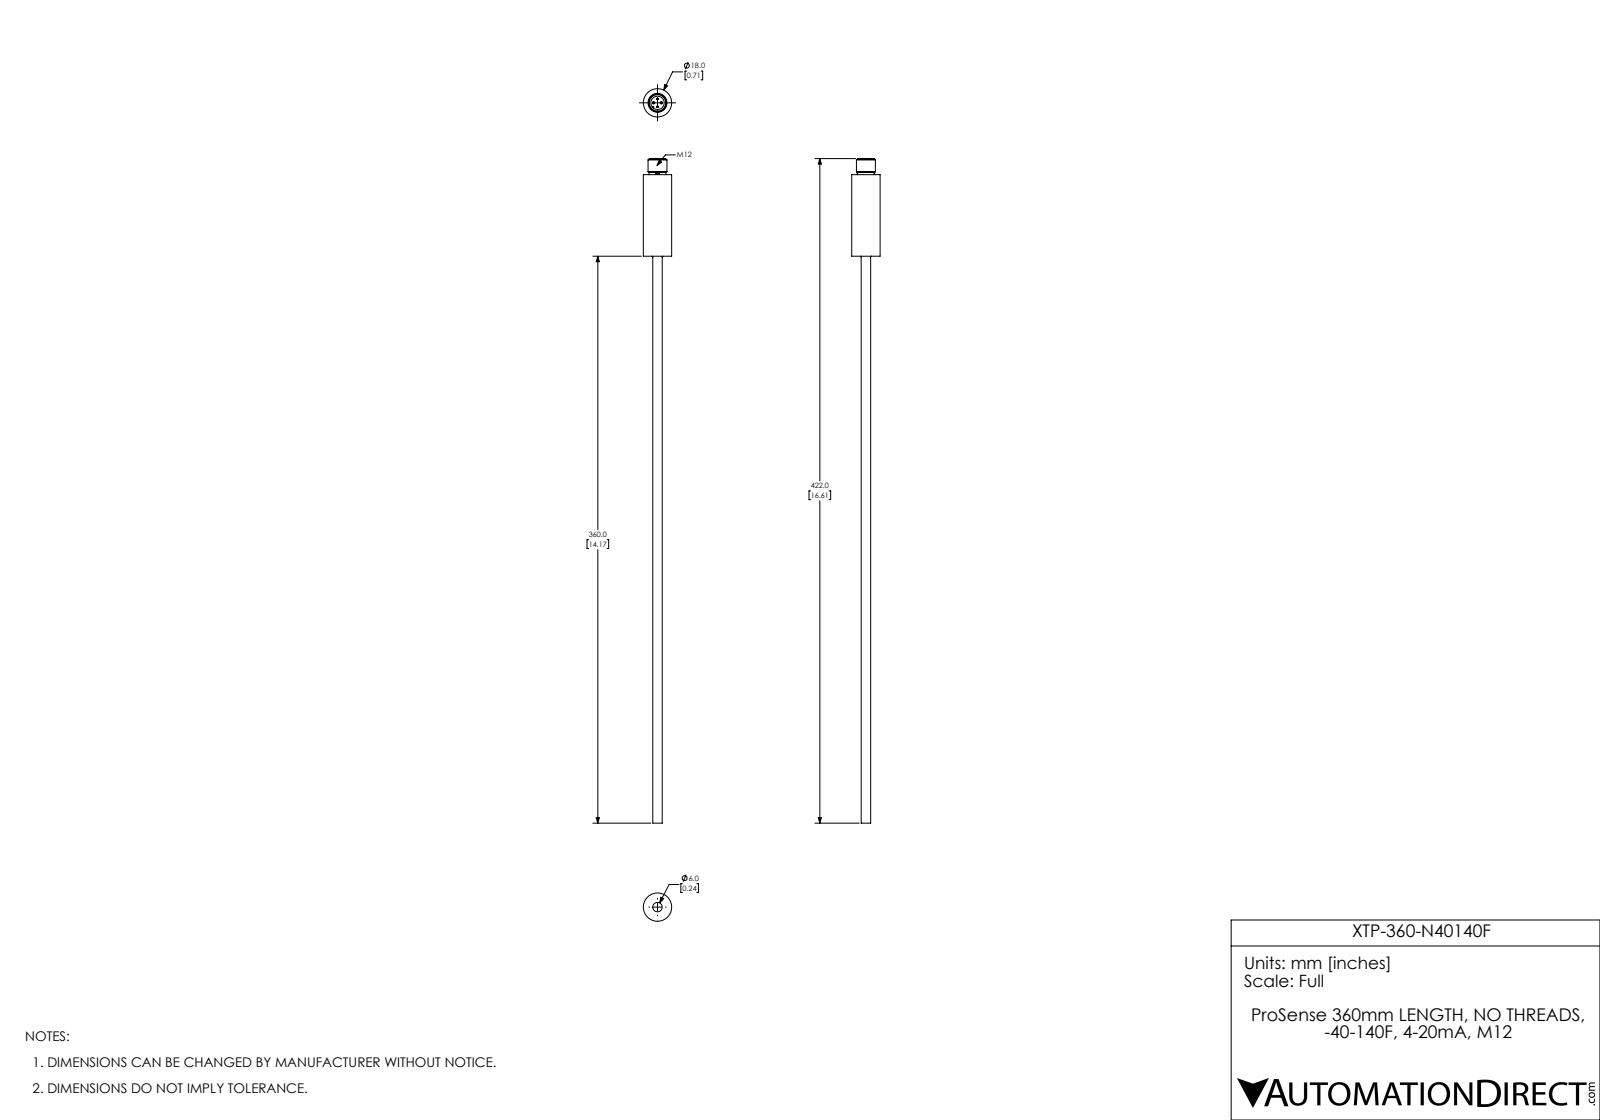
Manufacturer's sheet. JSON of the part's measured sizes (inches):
{"part_name": "XTP-360-N40140F", "step_written_by": "SolidWorks 2017 (AUTOMOTIVE_DESIGN)", "units": "inches", "bodies": {"solids": 1, "faces": 67, "planar": 24, "cylindrical": 21, "other": 22}, "overall_size": [16.614, 0.709, 0.709], "volume_in3": 1.463, "surface_area_in2": 16.93, "round_holes": [[0.335, 1]], "round_bosses_or_shafts": [[0.04, 4], [0.709, 1], [0.472, 1], [0.421, 1], [0.413, 1], [0.236, 1]], "partial_cylinders_radius": [[0.016, 1]], "face_to_face_distances": [2.039, 2.087, 0.047, 2.441, 0.402, 0.354, 14.173, 16.213, 16.26, 16.614]}
